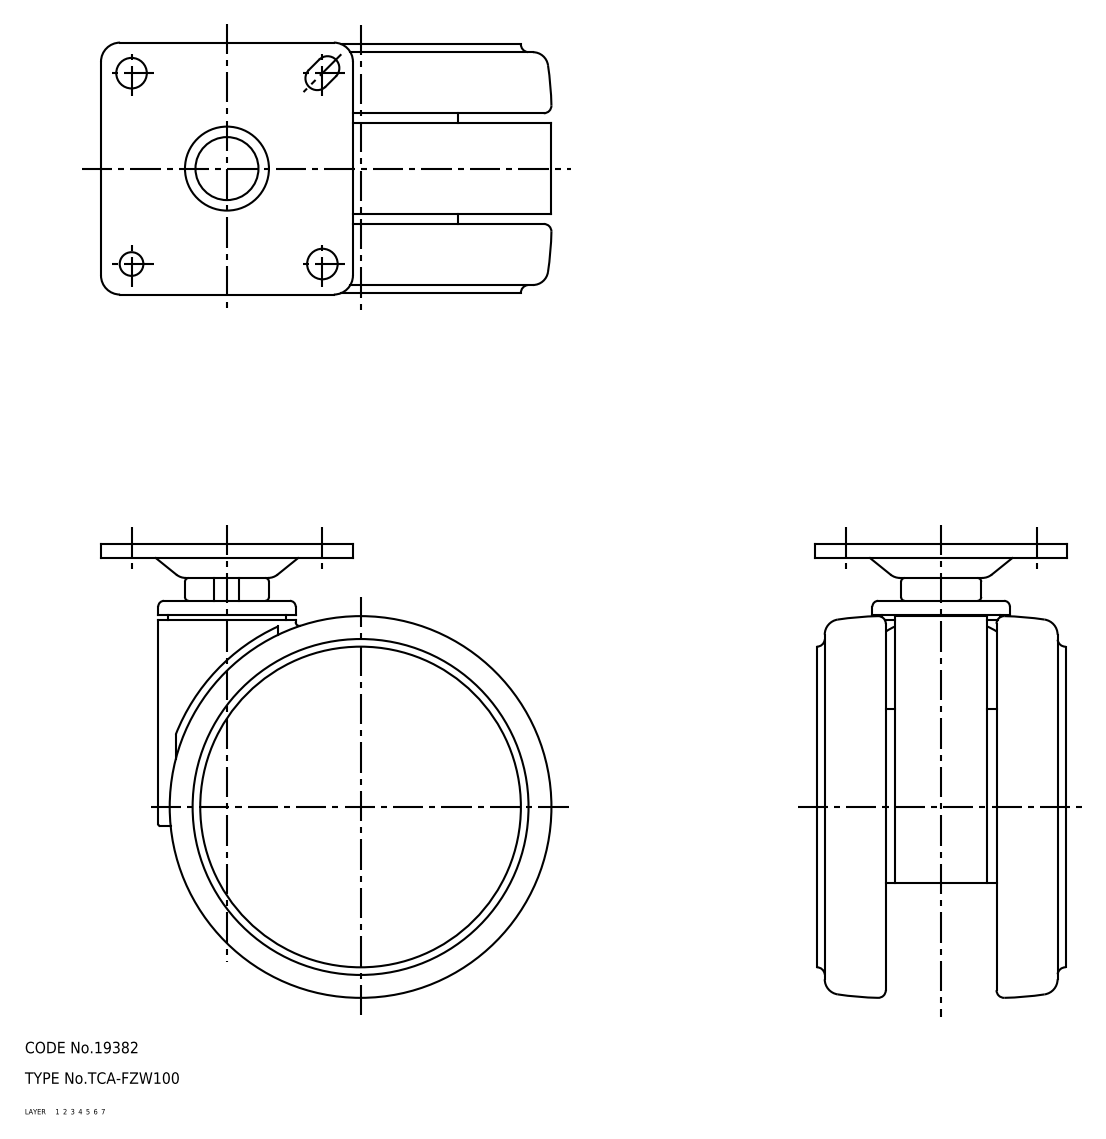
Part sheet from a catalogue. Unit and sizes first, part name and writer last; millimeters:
Units: millimetres
Overall size (bounding box): 119 × 118 × 66
Round holes (diameter × count): ⌀8 ×2, ⌀6.2 ×1, ⌀9.1 ×1, ⌀10 ×1, ⌀10.1 ×1, ⌀10.5 ×1, ⌀12 ×1, ⌀15 ×1, ⌀15.2 ×1, ⌀15.8 ×1, ⌀19.2 ×1, ⌀26 ×1
Round bosses / shafts (diameter × count): ⌀87.8 ×1, ⌀36 ×1, ⌀31 ×1, ⌀27.9 ×1, ⌀27.6 ×1, ⌀22 ×1, ⌀20 ×1, ⌀19 ×1
Partial cylindrical surfaces — rounded edges, fillets, slot ends (radius × count): R0.5 ×200, R1.2 ×160, R1 ×81, R0.2 ×16, R2 ×13, R0.3 ×12, R1.5 ×8, R0.8 ×6
Main face-to-face distances: 1.8, 61.6, 63.4, 3.6, 59.8, 14.5, 16.3, 13.25, 18.1, 47.1
Hole centre spacings: 35.36, 50, 70.71
Volume: 310 954 mm³ · Surface area: 131 619 mm²
Bodies: 1 solid, 2377 faces (801 planar, 1098 cylindrical, 478 other)
Part name (STEP PRODUCT): caster; TCA-FZW100
STEP written by: SolidWorks 2015 (AUTOMOTIVE_DESIGN)
